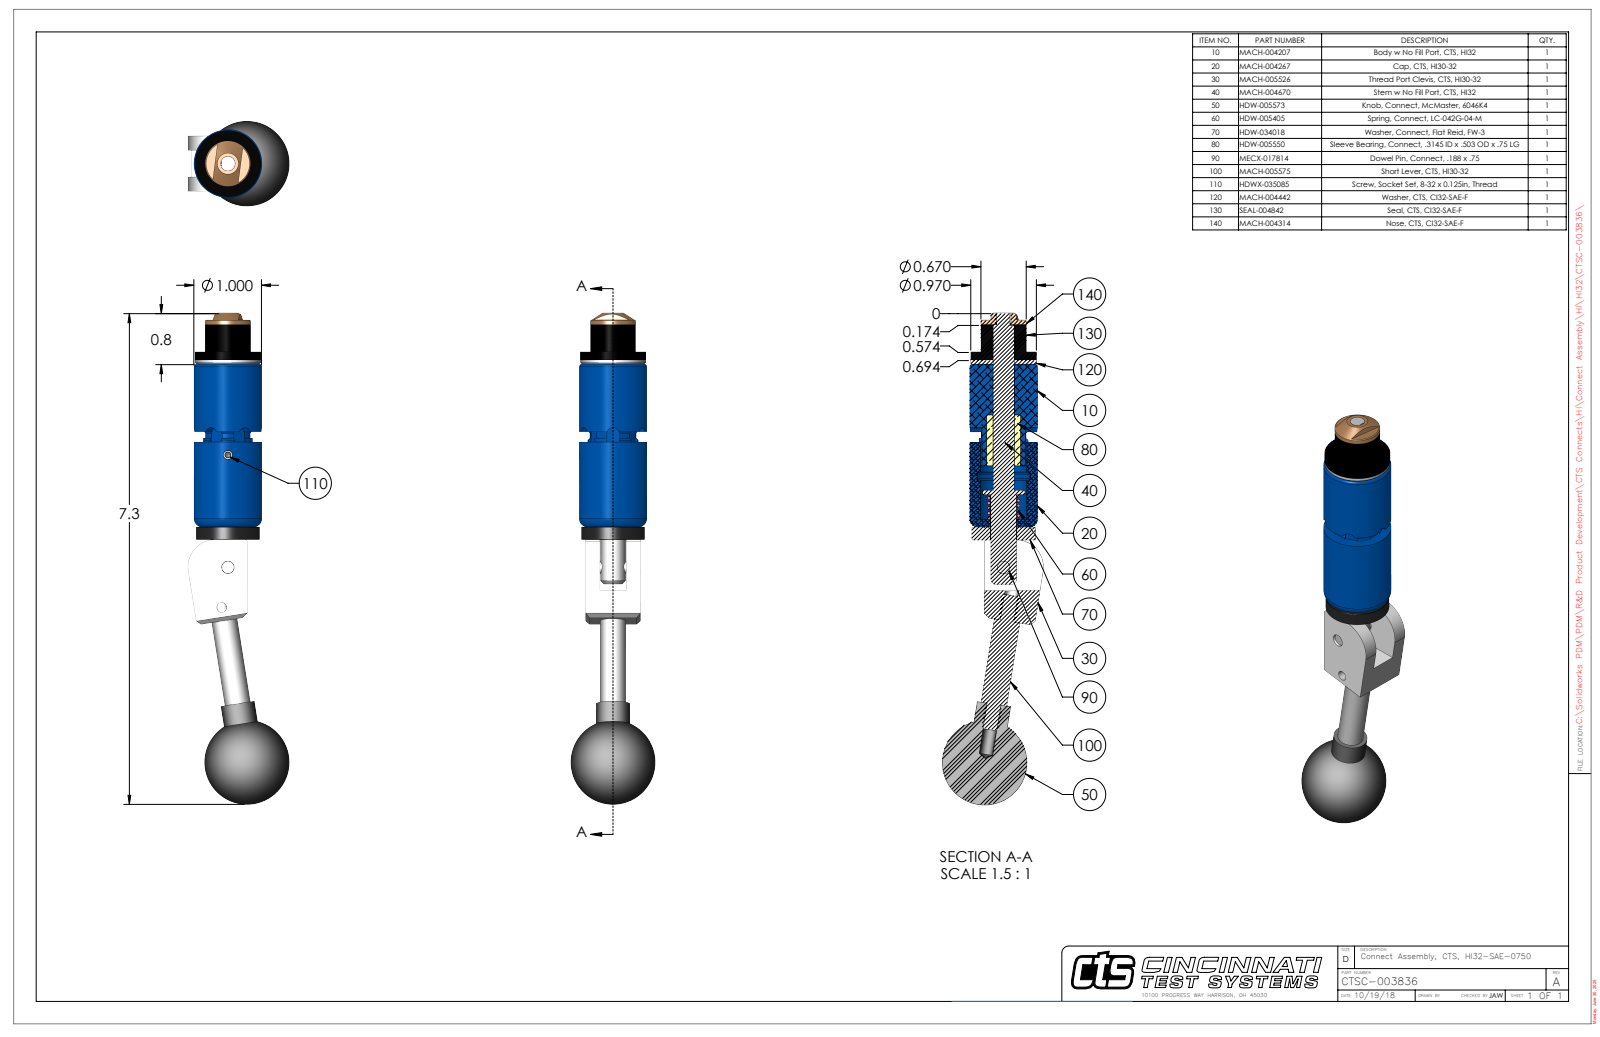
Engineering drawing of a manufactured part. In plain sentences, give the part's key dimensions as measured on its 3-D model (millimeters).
The part is named "CTSC-003836". Its 3-D file was written by "SolidWorks 2023 (AUTOMOTIVE_DESIGN)". It is 9 solids with 268 faces: 100 planar, 110 cylindrical and 58 other. Overall it measures 184.3 by 37.9 by 31.8 millimeters. Its volume is 66 470 cubic millimeters and its surface area 22 190 square millimeters. Round holes: 2 of diameter 5.1, 1 of diameter 3.5, 1 of diameter 3.8, 1 of diameter 4.8, 1 of diameter 5.4, 1 of diameter 7.9, 1 of diameter 8, 1 of diameter 8, 1 of diameter 9.8, 1 of diameter 10, 1 of diameter 17.5. Round bosses or shafts: 2 of diameter 6.4, 2 of diameter 5.1, 1 of diameter 25.4, 1 of diameter 24.6, 1 of diameter 23.8, 1 of diameter 17, 1 of diameter 12.7, 1 of diameter 9.7. Partial cylindrical surfaces (rounded edges, fillets, slot ends): 6 of radius 2.4, 2 of radius 0.7, 1 of radius 9.5, 1 of radius 10.2, 1 of radius 11.8. The main face-to-face distances are 1.5, 5.3, 15.3, 62.6, 61.1, 20.6, 67.4, 65.8, 4.7, 13.2. The hole center spacings are 15.2, 42.1, 57.2.
